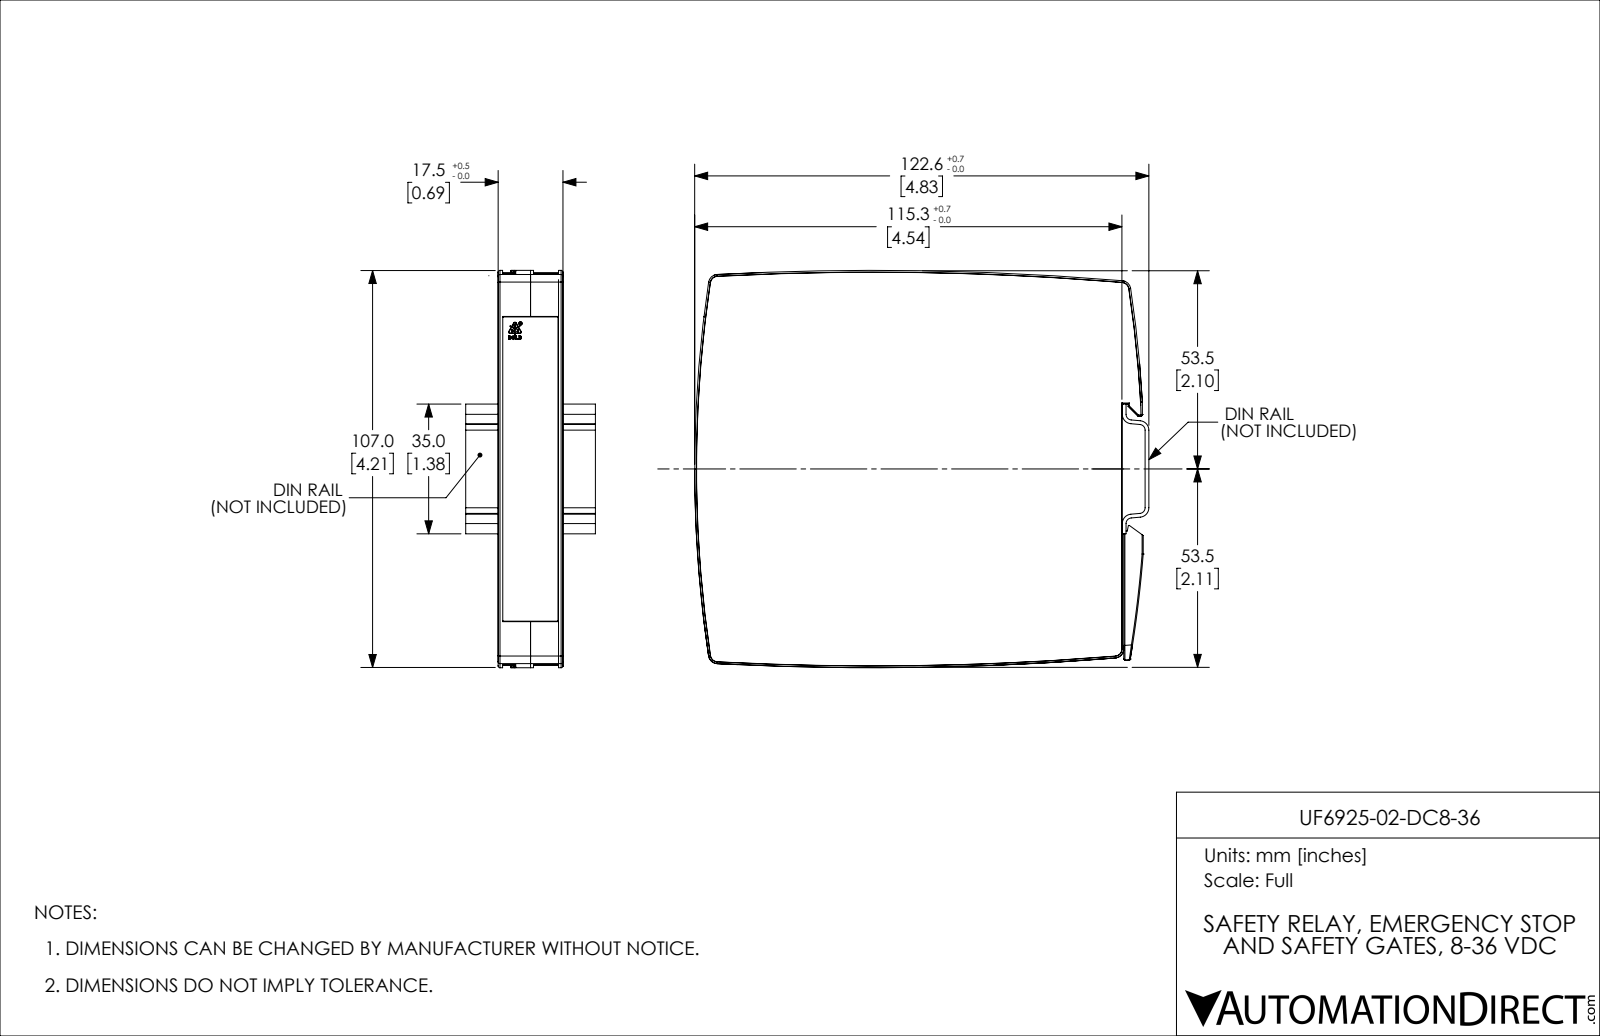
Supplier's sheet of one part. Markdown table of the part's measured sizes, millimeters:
| quantity | value |
| --- | --- |
| part name | UF6925-02-DC8-36 |
| STEP written by | SolidWorks 2018 (AUTOMOTIVE_DESIGN) |
| units | millimeters |
| bodies | 14 solids, 596 faces (376 planar, 87 cylindrical, 133 other) |
| overall size | 121.1 × 107.2 × 17.5 |
| volume | 44 430 mm³ |
| surface area | 66 710 mm² |
| round holes (diameter × count) | 0.9 × 1 |
| round bosses / shafts (diameter × count) | 0.9 × 1 |
| partial cylindrical surfaces (radius × count) | 0.1 × 8, 0.8 × 4, 0.4 × 3, 0.2 × 2, 0.4 × 2, 0.4 × 2, 803.8 × 2, 804.6 × 2 |
| main face-to-face distances | 1.2, 16.3, 17.5, 15.1, 8.7, 7.5, 2, 113.3, 111.3, 2 |
